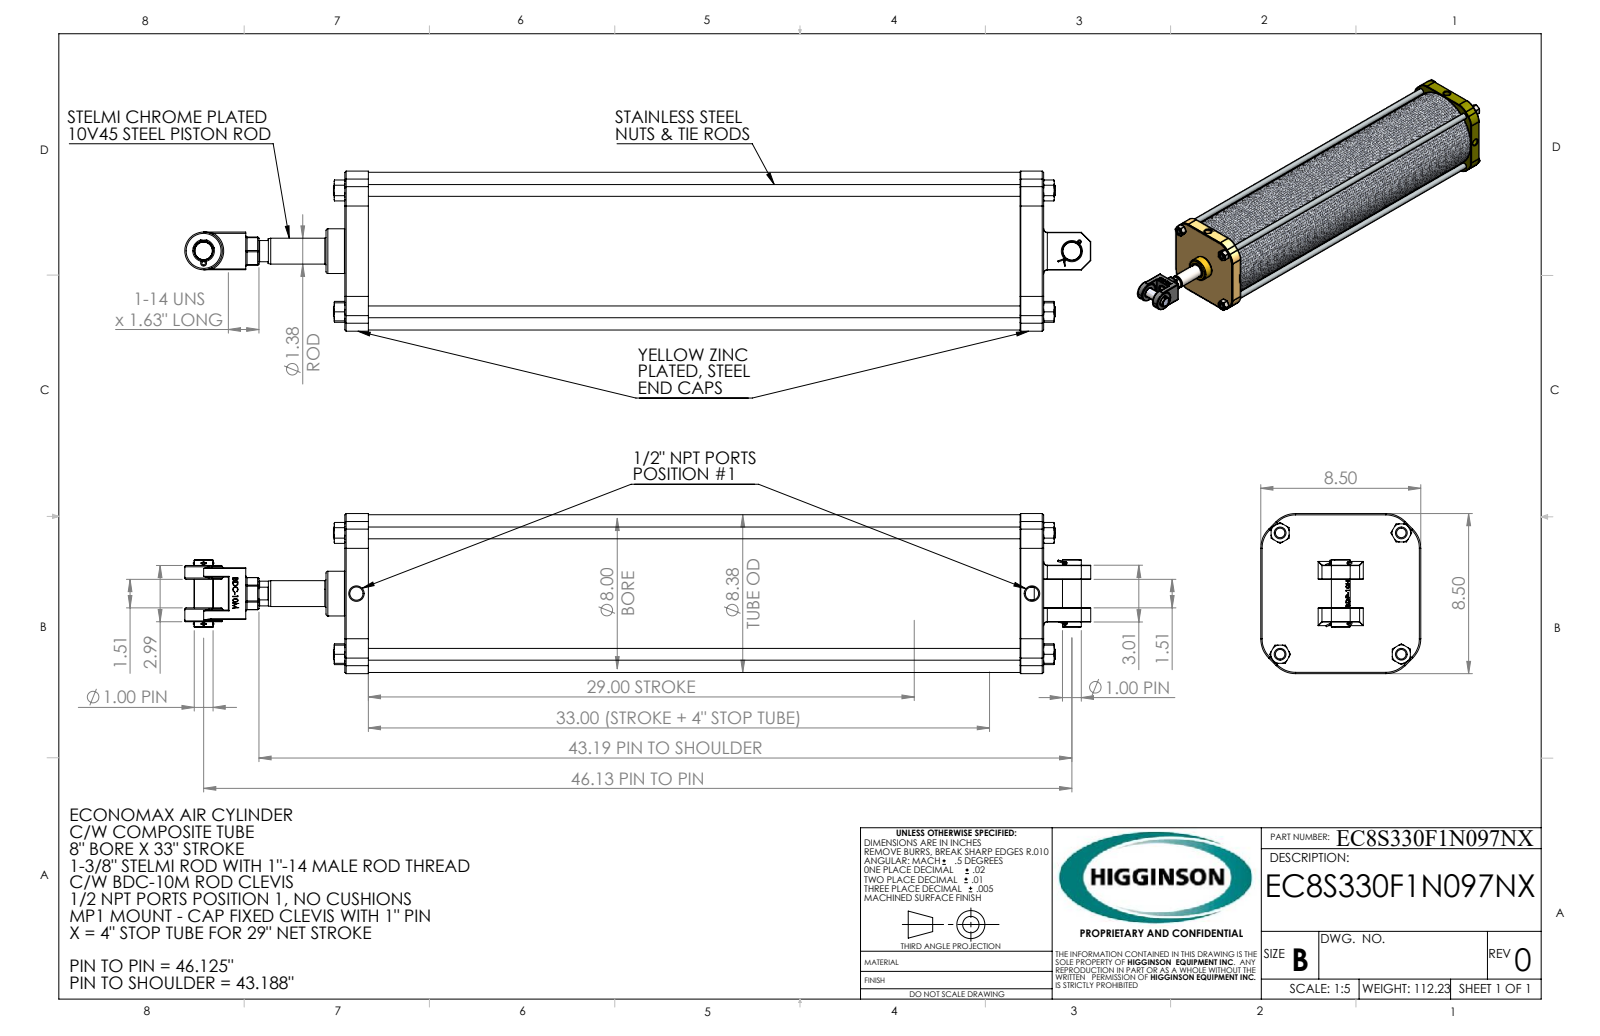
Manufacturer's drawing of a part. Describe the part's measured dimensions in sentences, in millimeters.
The part is named "8.0T33S LOGOTM; 1.38Rod4StopTube 33ES; BDC-10M; EC8S330F1N097NX (+8 more)". Its 3-D file was written by "SolidWorks 2021 (CONFIG_CONTROL_DESIGN)". It is 28 solids with 1482 faces: 359 planar, 302 cylindrical and 821 other. Overall it measures 1222.4 by 215.9 by 215.9 millimeters. Its volume is 9 134 000 cubic millimeters and its surface area 1 990 000 square millimeters. Round holes: 5 of diameter 3.6, 4 of diameter 15.9, 4 of diameter 16.7, 2 of diameter 17.8, 2 of diameter 17.9, 2 of diameter 25.5, 1 of diameter 16.4, 1 of diameter 25.4, 1 of diameter 35.2, 1 of diameter 35.3, 1 of diameter 38.4, 1 of diameter 41.4. Round bosses or shafts: 4 of diameter 1.5, 2 of diameter 25.4, 1 of diameter 212.6, 1 of diameter 203, 1 of diameter 202.7, 1 of diameter 196.7, 1 of diameter 191.1, 1 of diameter 63.5. Partial cylindrical surfaces (rounded edges, fillets, slot ends): 23 of radius 1.8, 20 of radius 0.5, 8 of radius 1, 8 of radius 36.8, 5 of radius 1, 4 of radius 4, 4 of radius 5.1, 2 of radius 1.8. The main face-to-face distances are 911.2, 31.8, 943, 879.5, 73, 870, 41.3, 838.2, 28.6, 215.9. The hole center spacings are 115.7, 163.6, 81.8, 1118.5, 81.8, 183.6, 185.2, 210.3.
